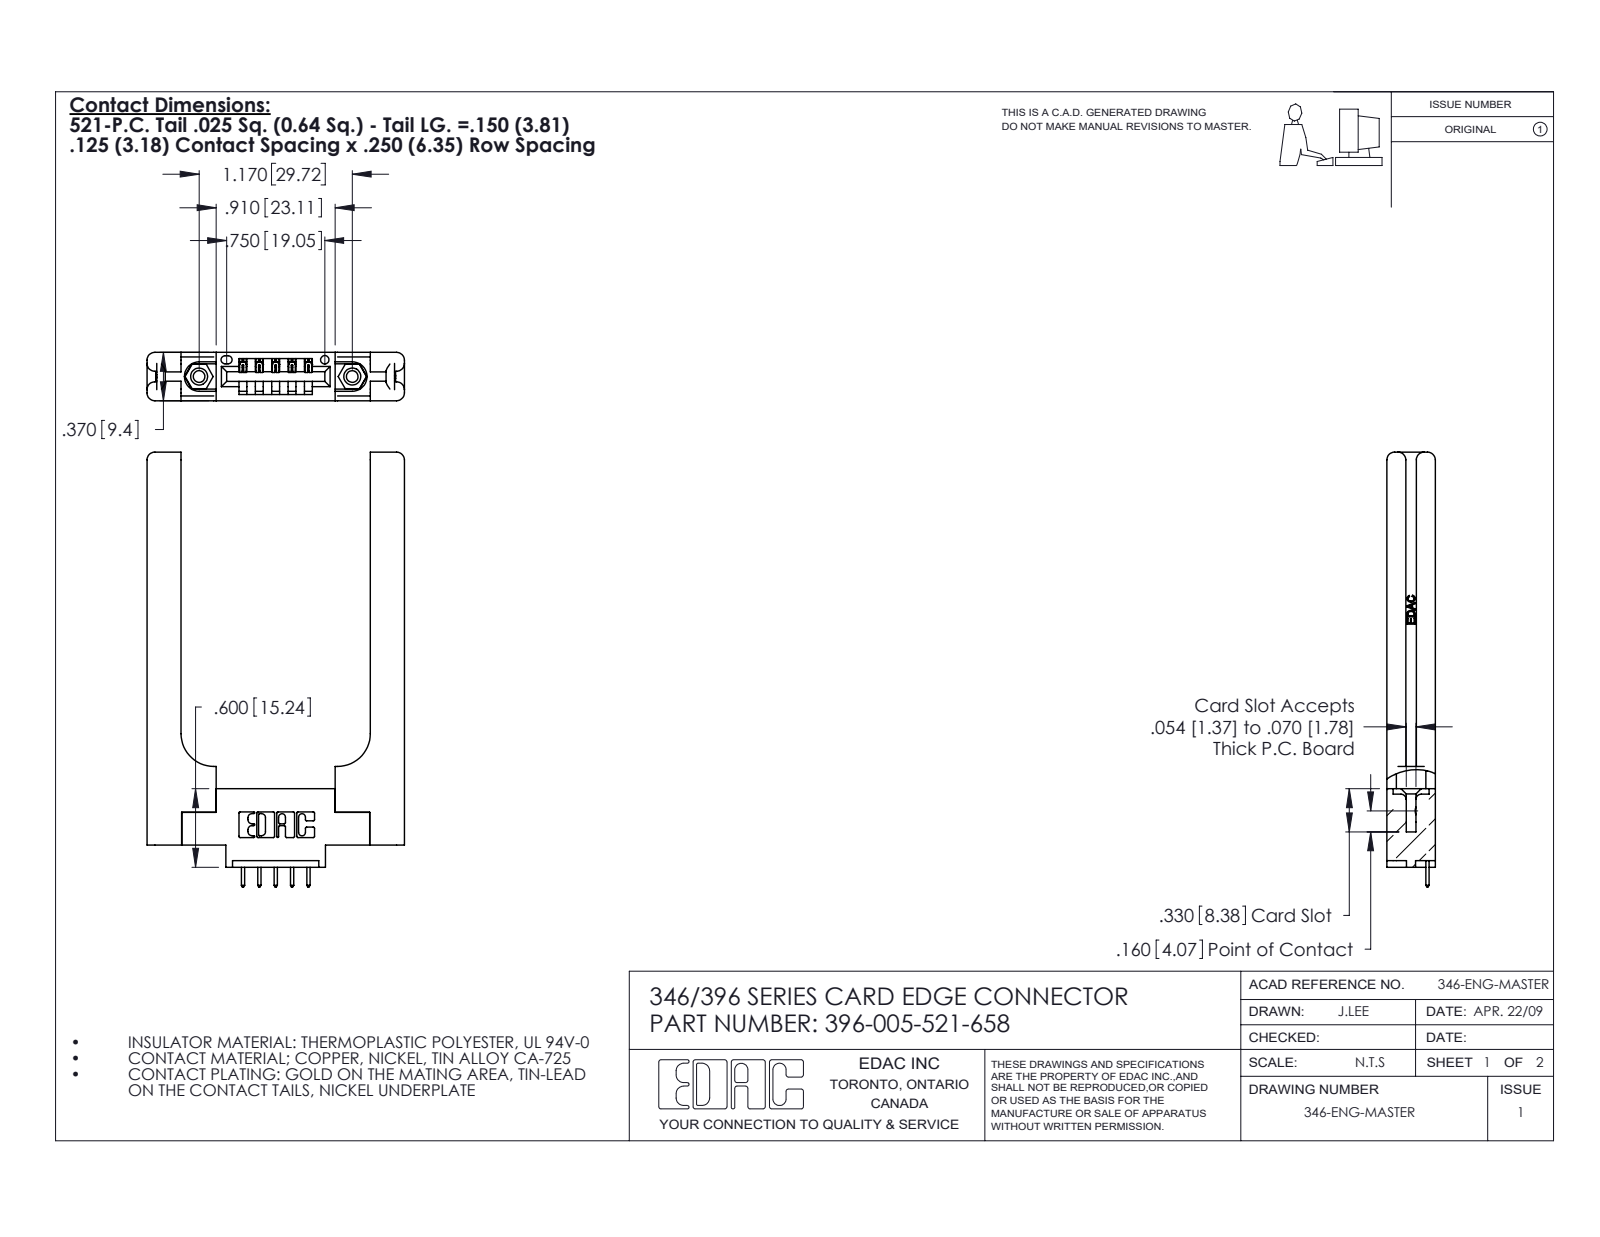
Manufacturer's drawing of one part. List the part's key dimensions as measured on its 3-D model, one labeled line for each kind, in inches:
Part name (STEP PRODUCT): 345-292-001_345-293-121; 346 Part_0.170 Offset - 0.156 Dia-TH; 396-005-521-658; 346-220-058_345-220-058 (+1 more)
STEP written by: SolidWorks 2020 (CONFIG_CONTROL_DESIGN)
Units: inches
Bodies: 10 solids, 686 faces (442 planar, 184 cylindrical, 60 other)
Overall size (bounding box): 3.32 × 1.966 × 0.37
Volume: 0.724 in³ · Surface area: 16.01 in²
Round holes (diameter × count): ⌀0.089 ×2, ⌀0.125 ×2, ⌀0.156 ×2, ⌀0.064 ×1
Round bosses / shafts (diameter × count): ⌀0.155 ×2
Partial cylindrical surfaces — rounded edges, fillets, slot ends (radius × count): R0.01 ×22, R0.06 ×16, R0.006 ×10, R0.01 ×10, R0.007 ×6, R0.031 ×6, R0.026 ×3, R0.03 ×2
Main face-to-face distances: 0.37, 0.15, 0.22, 0.072, 1.446, 0.25, 0.148, 0.075, 0.071, 0.26
Hole centre spacings: 0.246, 0.969, 1.17
